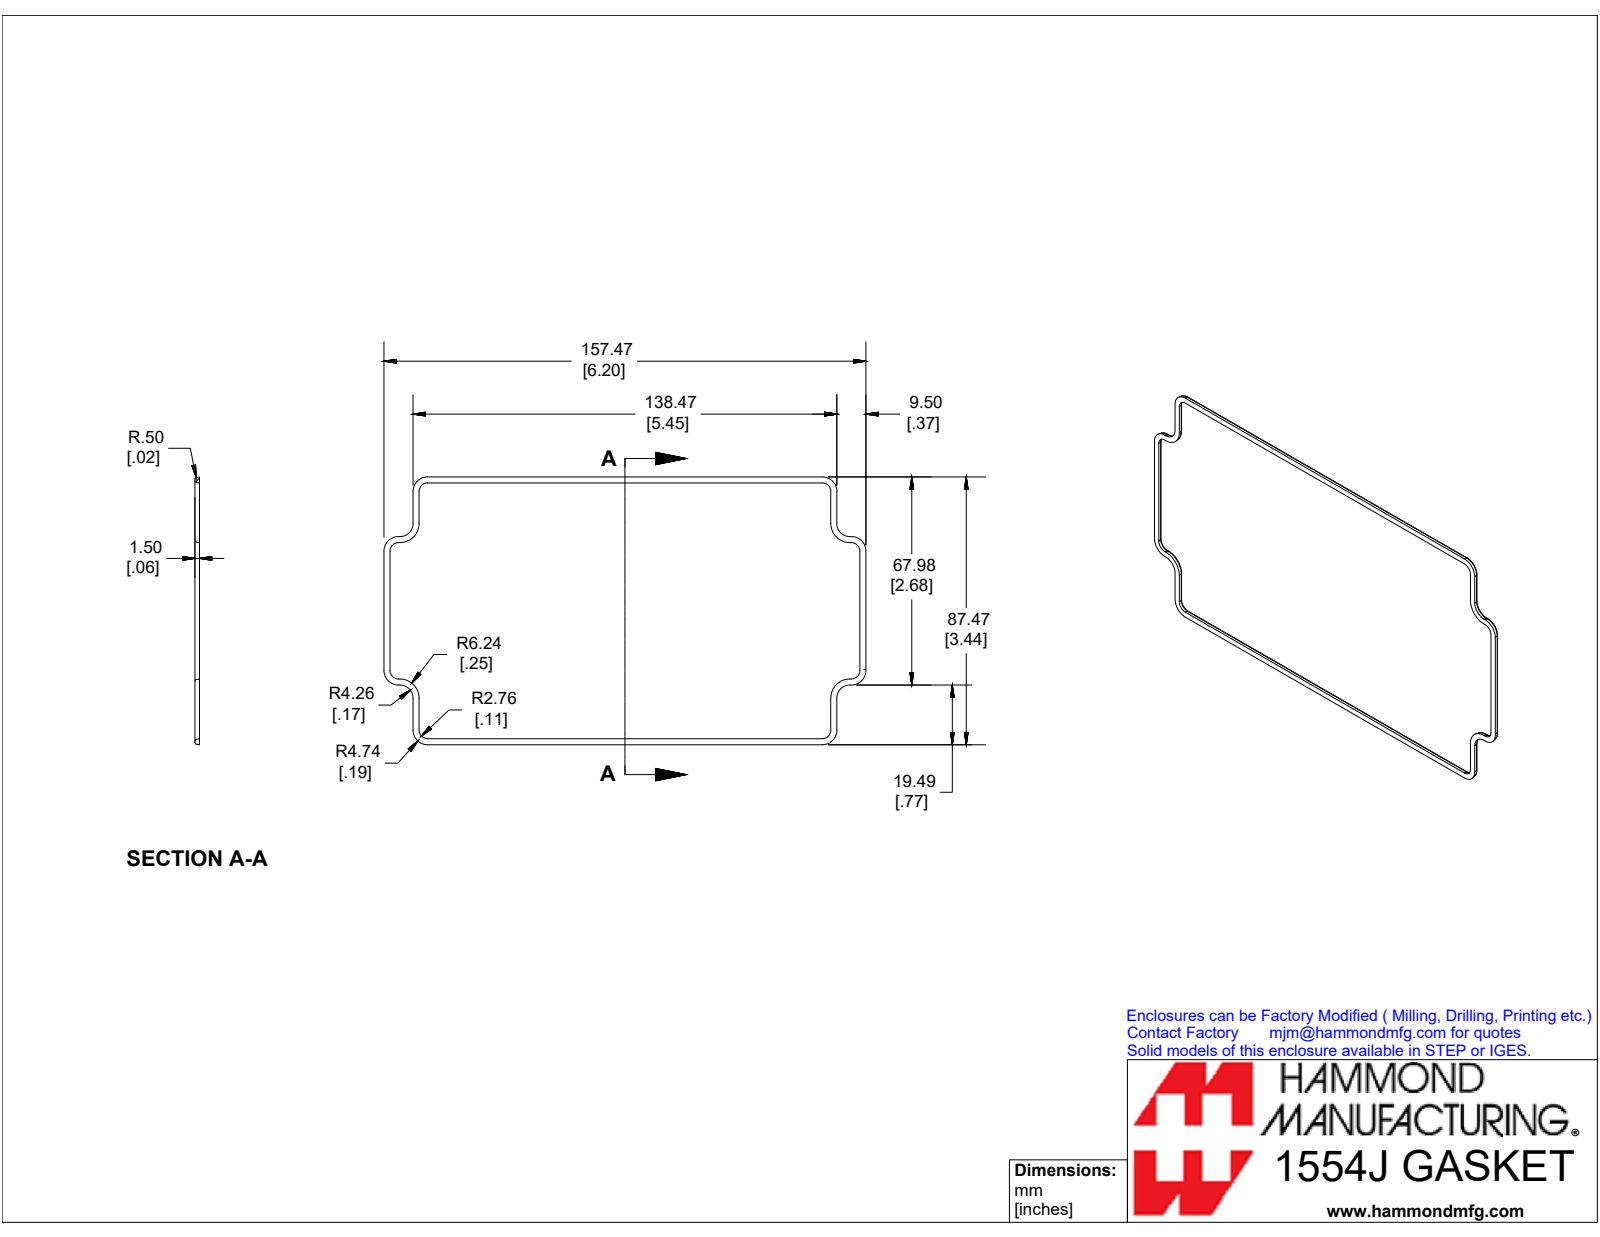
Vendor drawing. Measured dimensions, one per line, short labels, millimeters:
name: 1554JGASKET
written by: SolidWorks 2019 (CONFIG_CONTROL_DESIGN)
unit: mm
bodies: 1 solid, 96 faces (25 planar, 23 cylindrical, 48 other)
size: 157.5 × 87.5 × 1.5
volume: 1 100 mm³; area: 2 843 mm²
rounds: 16× R0.5
face distances: 1.5, 84.2, 84.2, 9.4, 143.8, 153.2, 134.4, 65, 19.2, 19.2
